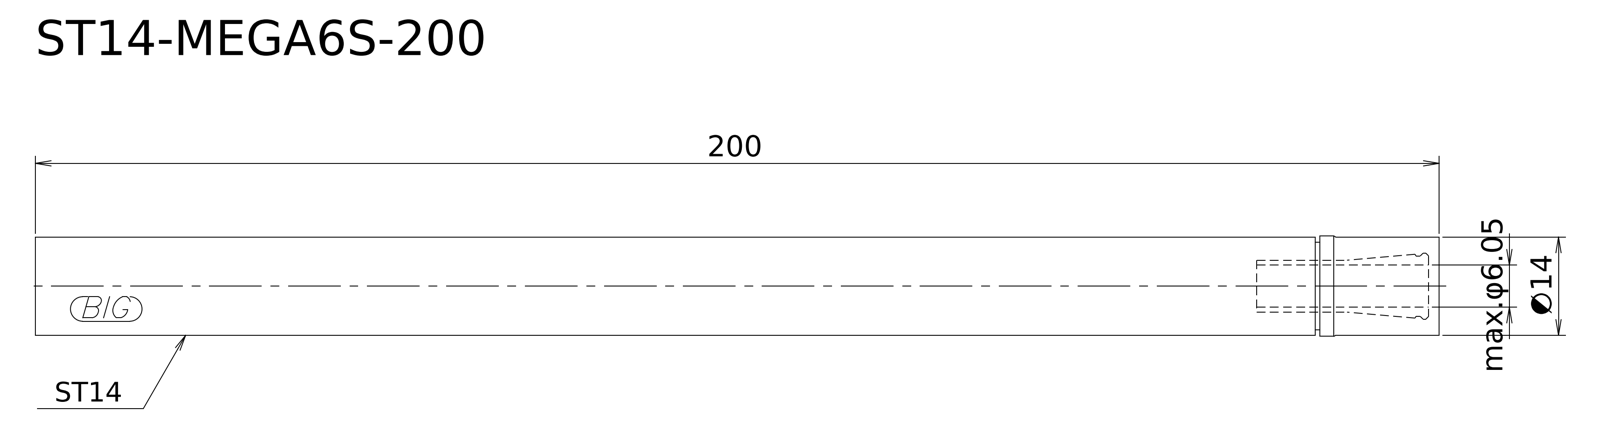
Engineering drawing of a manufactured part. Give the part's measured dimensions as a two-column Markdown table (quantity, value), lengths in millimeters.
| quantity | value |
| --- | --- |
| STEP written by | Kubotek KeyCreator V8.5.1 (14335) (CONFIG_CONTROL_DESIGN) |
| units | millimeters |
| bodies | 1 solid, 9 faces (3 planar, 4 cylindrical, 2 other) |
| overall size | 200 × 14.3 × 14.3 |
| volume | 30 774 mm³ |
| surface area | 9 160 mm² |
| round bosses / shafts (diameter × count) | 14.3 × 1, 14 × 1, 12.5 × 1 |
| main face-to-face distances | 200, 17, 183 |
